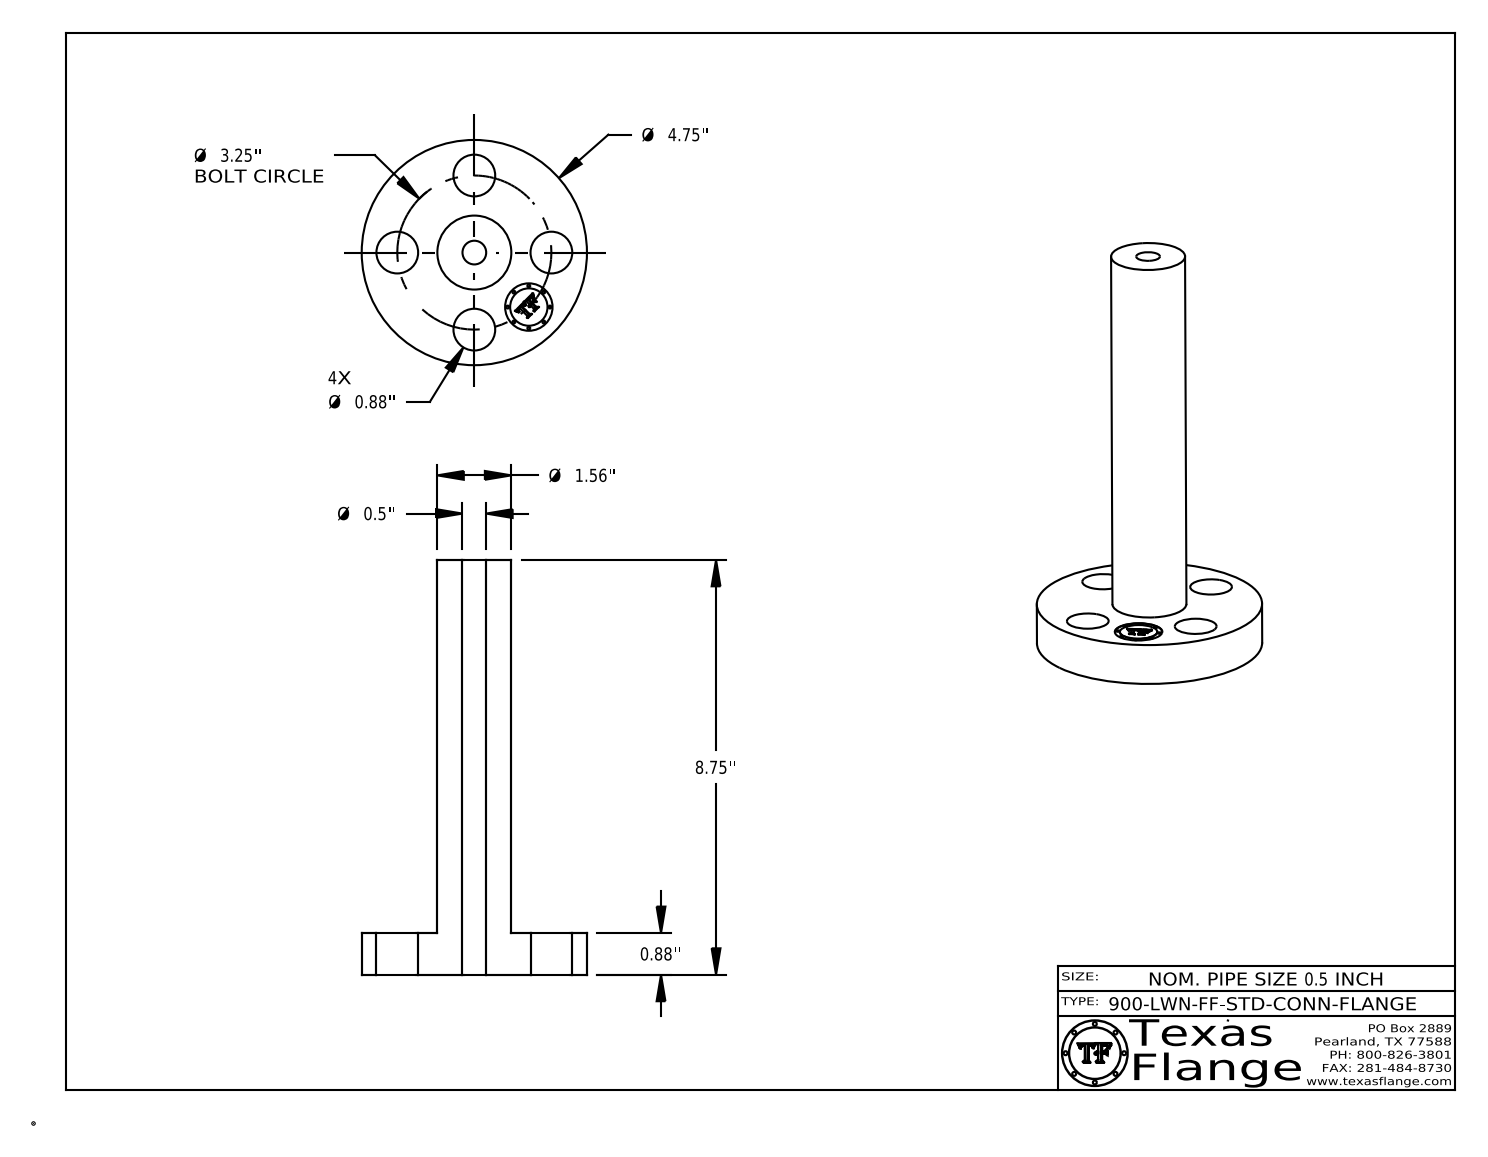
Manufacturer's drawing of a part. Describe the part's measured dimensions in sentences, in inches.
The part is named "0.5-900-LWN-FF-STD-CONN-FLANGE". Its 3-D file was written by "CATIA V5 STEP AP214 (AUTOMOTIVE_DESIGN)". It is 1 solid with 402 faces: 368 planar, 34 cylindrical and 0 other. Overall it measures 8.75 by 4.75 by 4.75 inches. Its volume is 26.78 cubic inches and its surface area 105.4 square inches. Round holes: 4 of diameter 0.88, 1 of diameter 0.5, 1 of diameter 1. Round bosses or shafts: 8 of diameter 0.061, 1 of diameter 4.75, 1 of diameter 1.56, 1 of diameter 0.788. The main face-to-face distances are 0.88, 8.75, 7.87, 0.875, 7.875, 0.298, 0.292, 0.054, 0.193, 0.248. The hole center spacings are 1.625, 2.298, 1.244, 3.003, 3.25.
